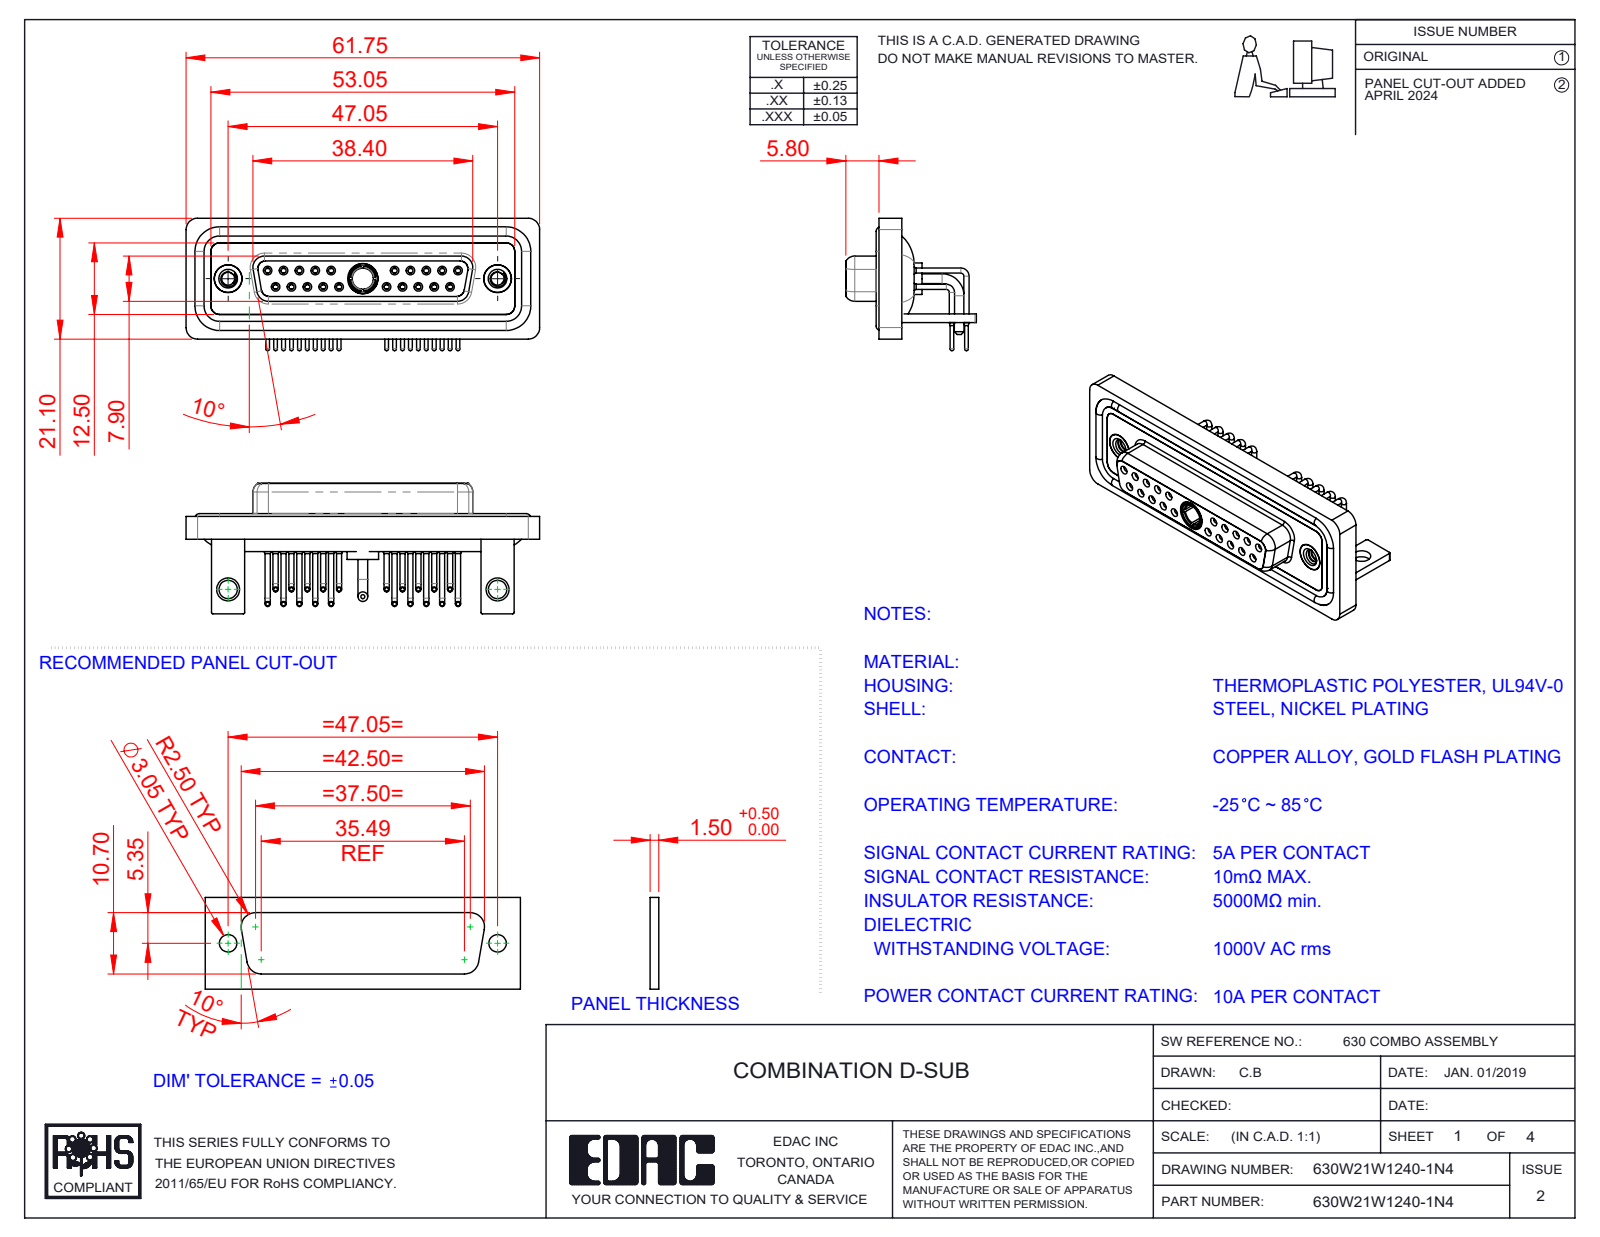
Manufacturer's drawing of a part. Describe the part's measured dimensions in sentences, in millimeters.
The part is named "630Combo Shell Front_25 Contacts; 630Combo Contact Row 1_50 Contacts; 630Combo Shell Rear_25 Contacts; 630W21W1140-1N4 (+6 more)". Its 3-D file was written by "SolidWorks 2023 (CONFIG_CONTROL_DESIGN)". It is 31 solids with 1572 faces: 454 planar, 697 cylindrical and 421 other. Overall it measures 61.75 by 23.12 by 22.8 millimeters. Its volume is 8 814 cubic millimeters and its surface area 15 464 square millimeters. Round holes: 20 of diameter 0.9, 20 of diameter 1.1, 20 of diameter 1.5, 20 of diameter 2, 10 of diameter 1.6, 10 of diameter 1.7, 3 of diameter 4.85, 2 of diameter 2.26, 2 of diameter 3.2, 2 of diameter 4, 2 of diameter 4.05, 2 of diameter 5. Round bosses or shafts: 20 of diameter 0.9, 20 of diameter 0.65, 14 of diameter 1.6, 2 of diameter 4.95, 2 of diameter 4.8, 2 of diameter 1.7, 1 of diameter 5.5, 1 of diameter 5.2. Partial cylindrical surfaces (rounded edges, fillets, slot ends): 19 of radius 2, 18 of radius 1.5, 16 of radius 0.25, 8 of radius 1.35, 8 of radius 1.6, 5 of radius 0.5, 4 of radius 0.6, 4 of radius 0.65. The main face-to-face distances are 0.4, 1.8, 2.9, 3.7, 1.5, 4.1, 1.1, 1.4, 1.6, 2.5. The hole center spacings are 3.16, 2.77, 5.54, 8.31, 5.04, 19.39, 20.97, 22.16.
